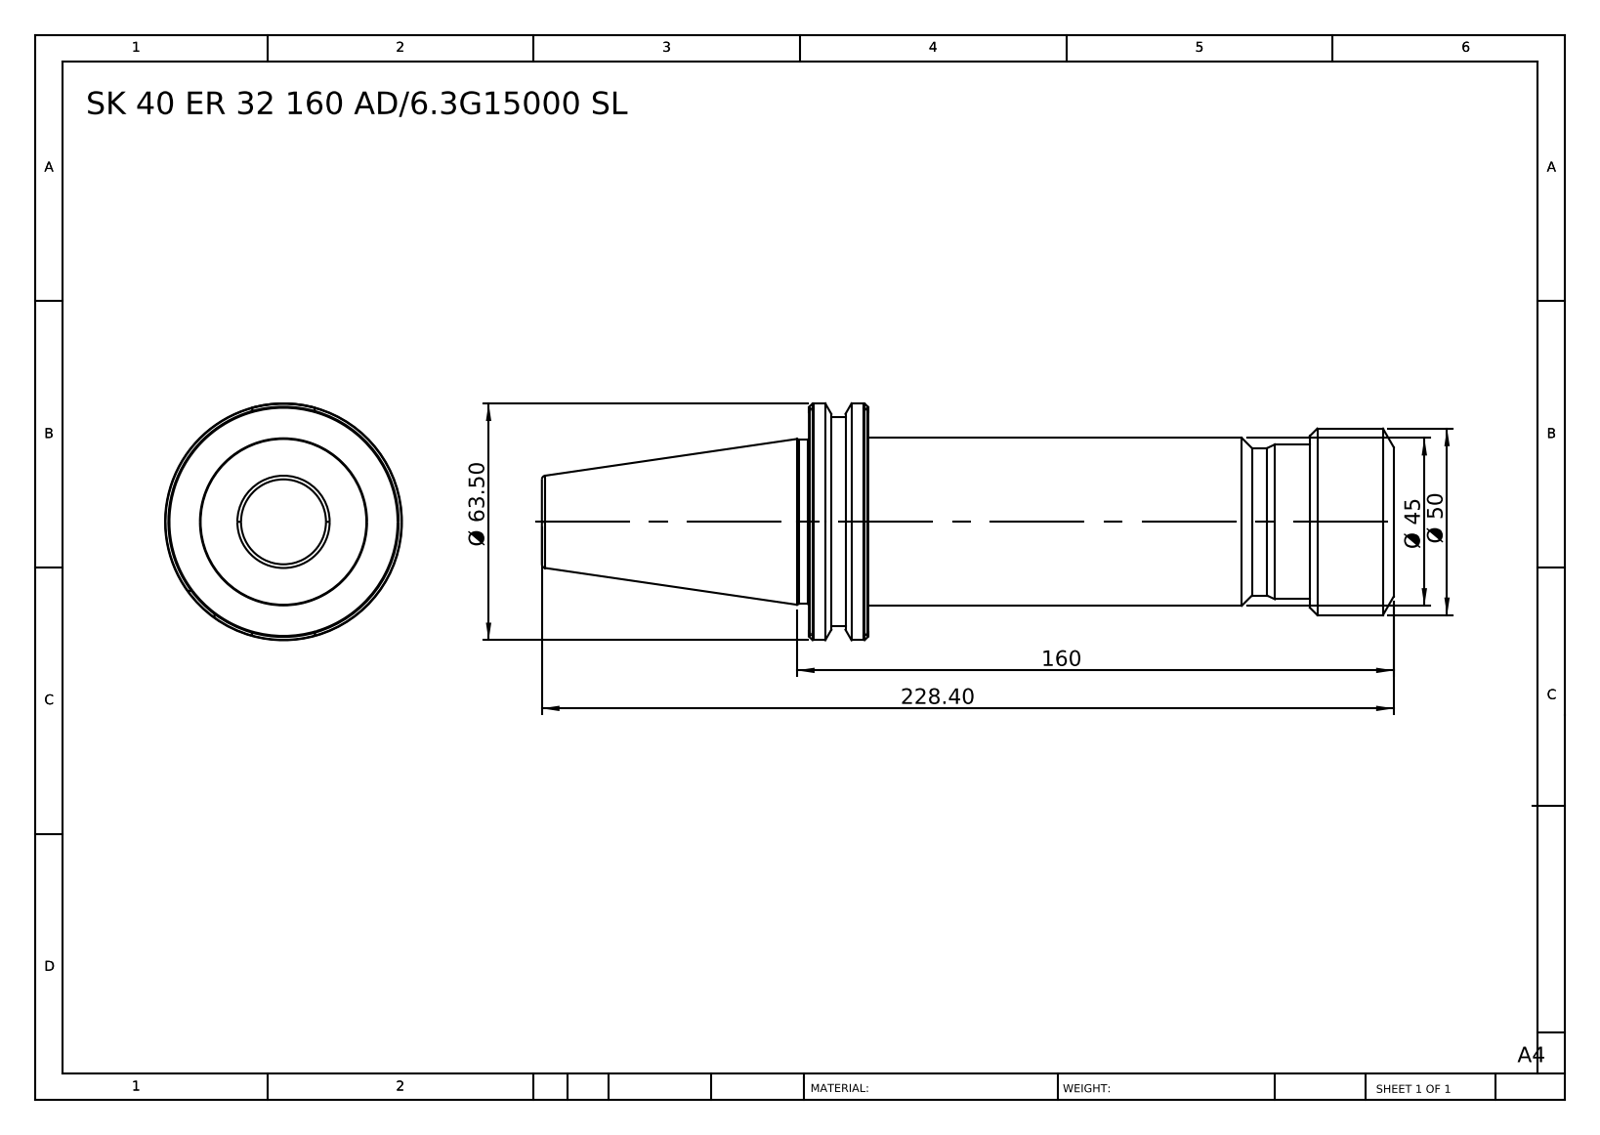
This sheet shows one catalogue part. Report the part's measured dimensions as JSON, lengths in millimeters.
{"part_name": "SK 40 ER 32 160 AD-6.3G15000 SL", "step_written_by": "SolidWorks 2014 (CONFIG_CONTROL_DESIGN)", "units": "millimeters", "bodies": {"solids": 1, "faces": 84, "planar": 7, "cylindrical": 16, "other": 61}, "overall_size": [228.4, 63.5, 63.5], "volume_mm3": 343384, "surface_area_mm2": 37610, "round_bosses_or_shafts": [[63.5, 1], [56, 1], [50, 1], [45, 1], [44, 1], [41.5, 1], [39.5, 1]], "face_to_face_distances": [15.9, 140.9, 156.8, 228.4, 87.5, 71.6, 22.5, 118.4, 134.3, 205.9]}
